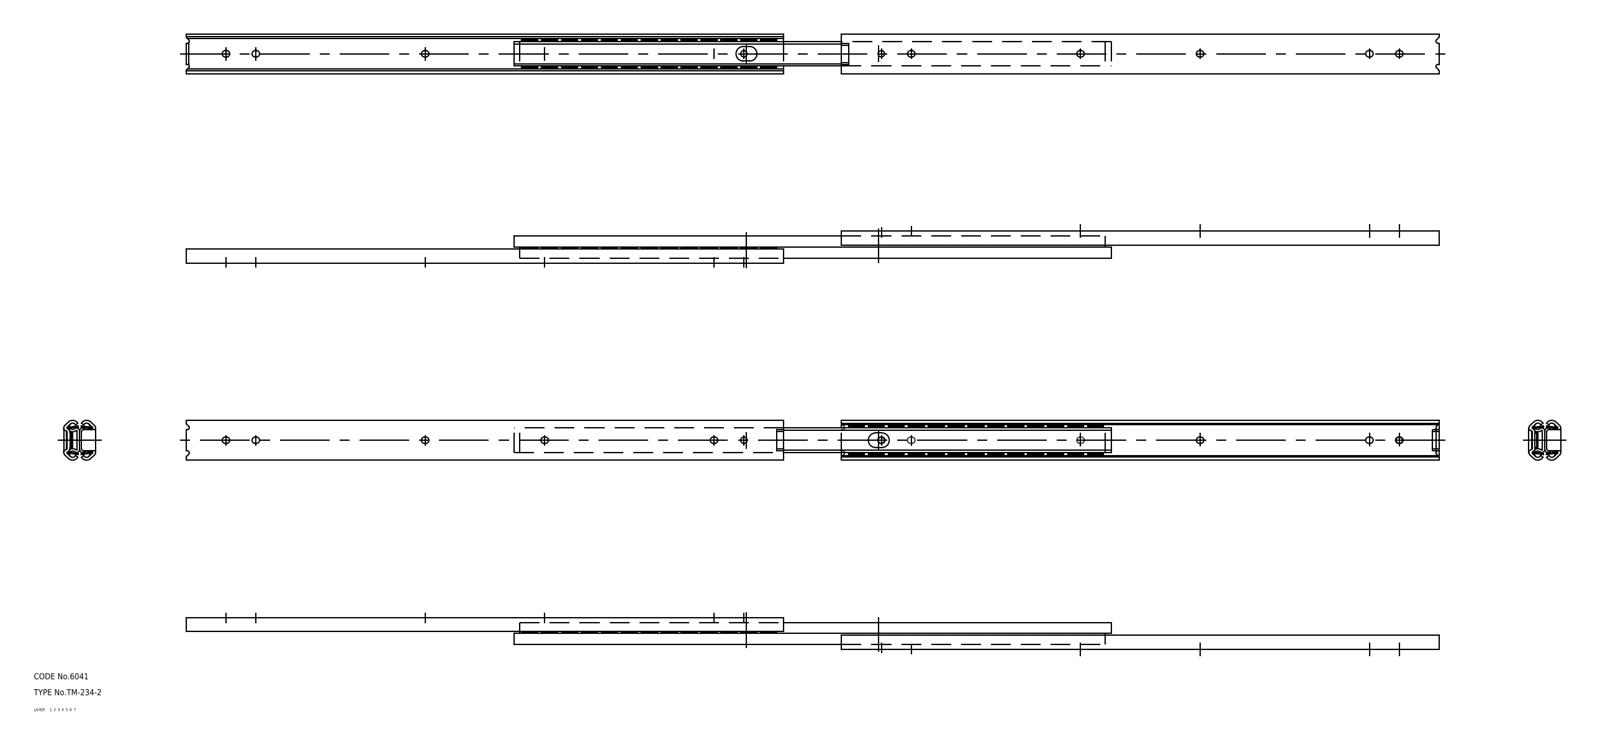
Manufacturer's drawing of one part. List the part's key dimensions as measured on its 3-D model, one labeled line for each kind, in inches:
Part name (STEP PRODUCT): ball; retainer; member_A; member_B (+1 more)
STEP written by: CADfix (AUTOMOTIVE_DESIGN)
Units: inches
Bodies: 57 solids, 792 faces (0 planar, 0 cylindrical, 792 other)
Overall size (bounding box): 24.764 × 0.787 × 0.63
Volume: 2.453 in³ · Surface area: 105.5 in²
